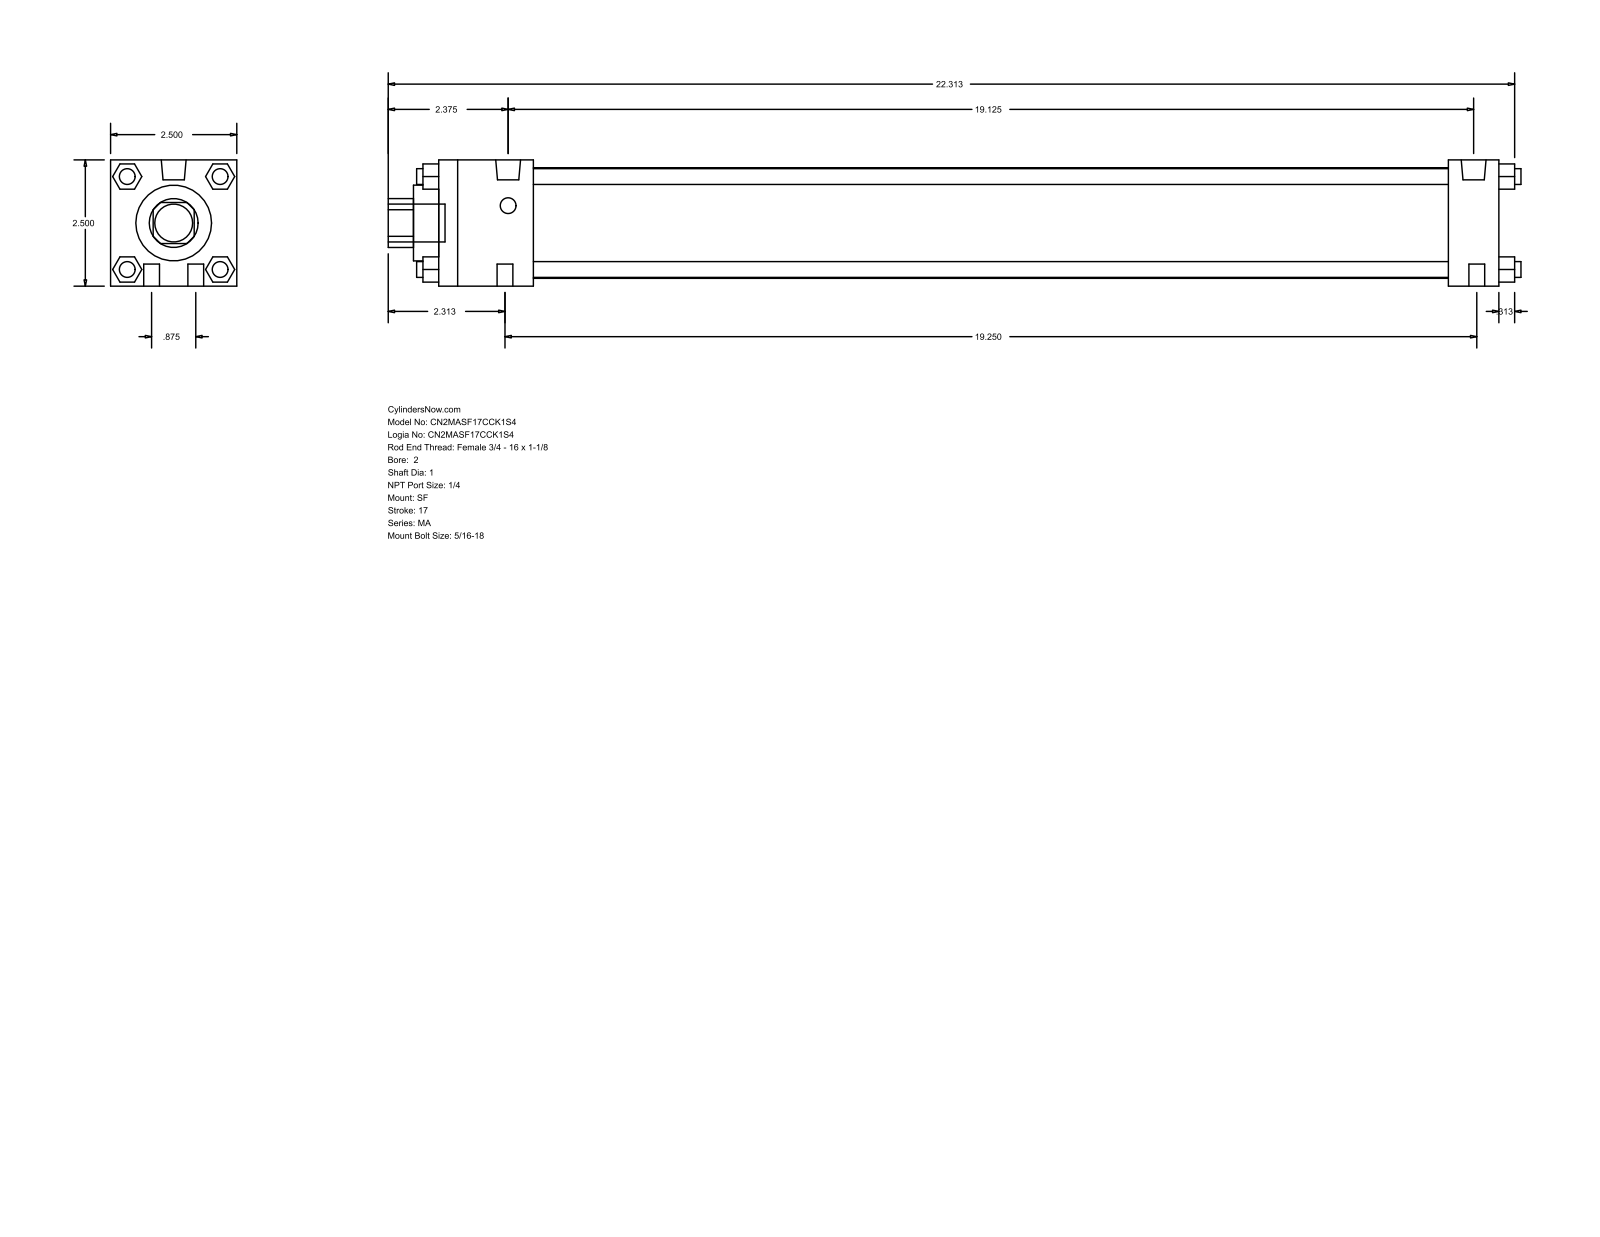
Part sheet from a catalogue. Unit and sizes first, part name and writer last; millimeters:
Units: millimetres
Overall size (bounding box): 569.91 × 63.5 × 63.5
Round holes (diameter × count): ⌀25.4 ×1, ⌀38.1 ×1, ⌀55.63 ×1
Round bosses / shafts (diameter × count): ⌀7.94 ×10, ⌀12.49 ×2, ⌀19.05 ×1
Partial cylindrical surfaces — rounded edges, fillets, slot ends (radius × count): R12.29 ×1
Main face-to-face distances: 63.5, 533.4, 12.7, 25.4, 508, 47.63, 460.37, 485.77, 40.47, 23.37
Bodies: 0 solids, 124 faces (94 planar, 30 cylindrical, 0 other)
Part name (STEP PRODUCT): MA_SF__0200_1
STEP written by: GSSL Pune (CONFIG_CONTROL_DESIGN)
